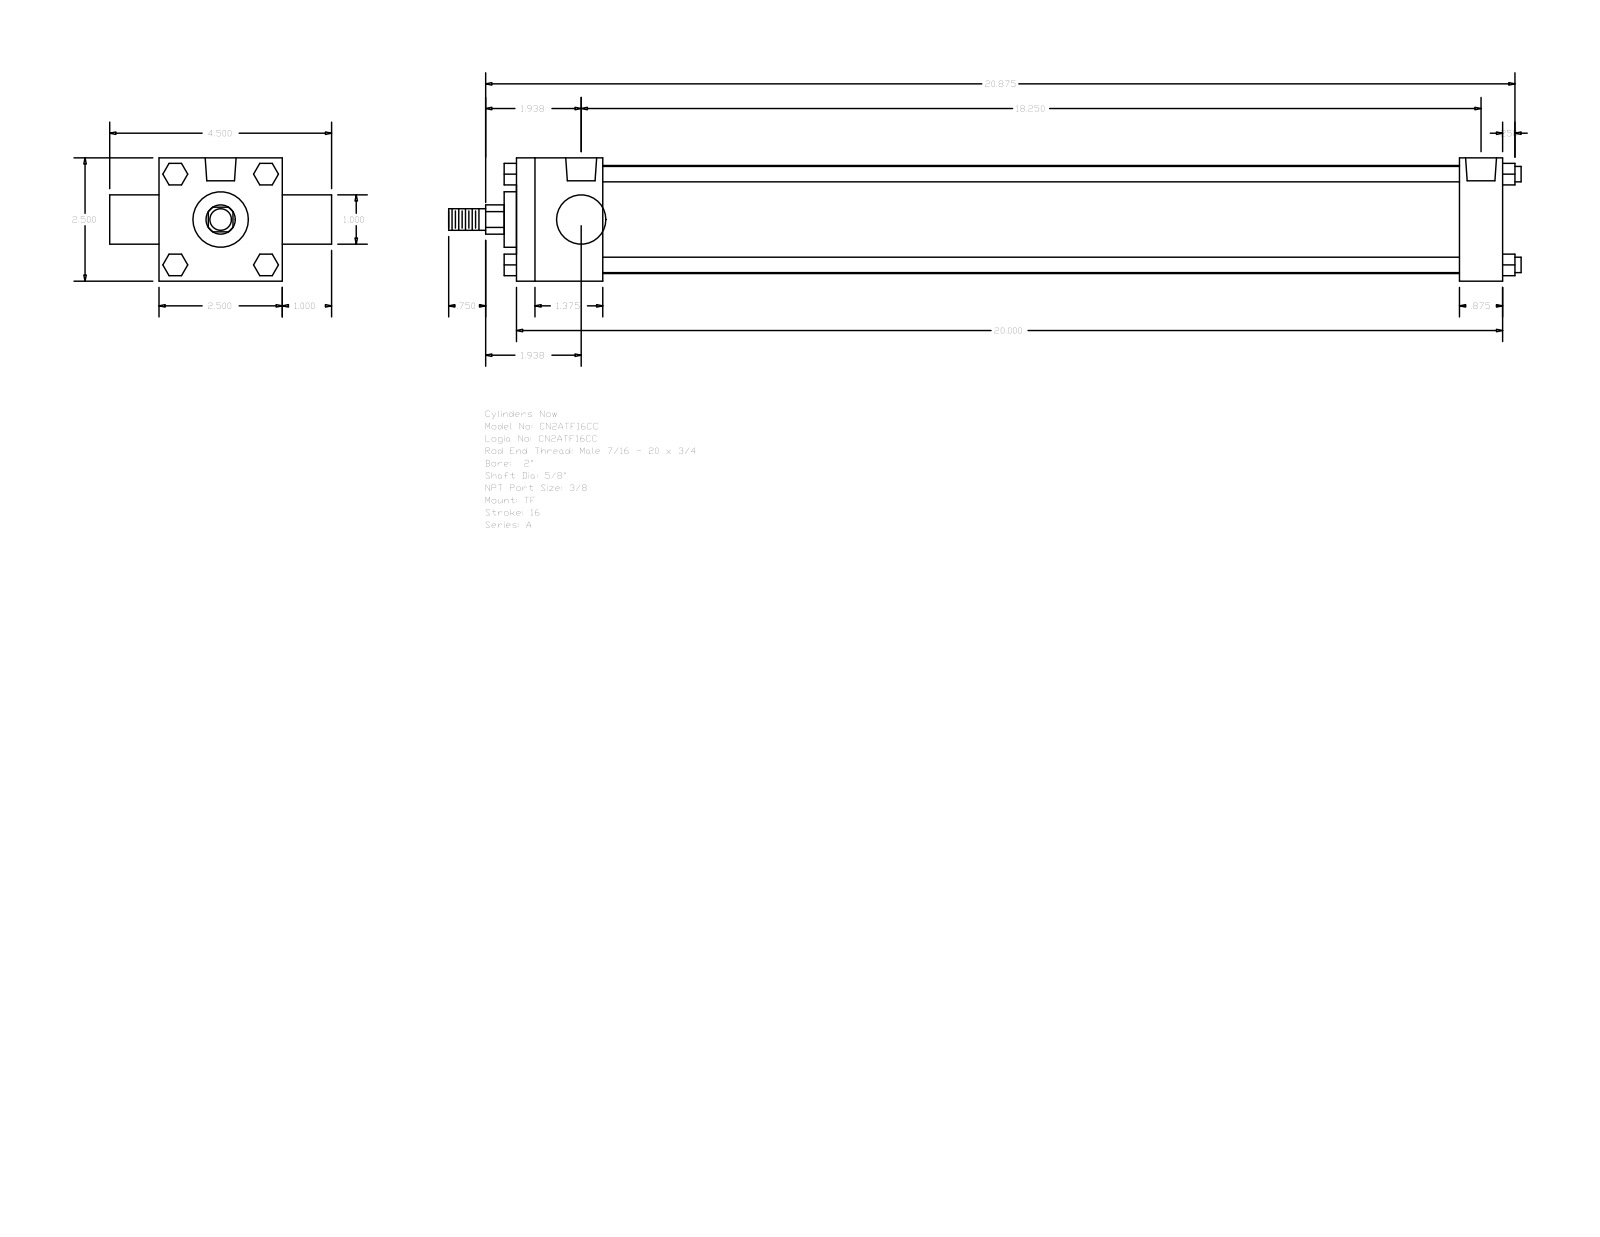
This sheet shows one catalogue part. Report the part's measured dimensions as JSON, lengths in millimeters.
{"part_name": "A_TF__0200_0.625", "step_written_by": "GSSL Pune (CONFIG_CONTROL_DESIGN)", "units": "millimeters", "bodies": {"solids": 0, "faces": 120, "planar": 92, "cylindrical": 28, "other": 0}, "overall_size": [552.45, 114.3, 63.5], "round_holes": [[5.56, 3], [15.93, 2]], "round_bosses_or_shafts": [[7.94, 4], [55.63, 1], [28.57, 1], [25.4, 1], [15.88, 1], [11.11, 1]], "partial_cylinders_radius": [[7.54, 1]], "face_to_face_distances": [63.5, 508, 44.45, 485.77, 441.32, 463.55, 22.23, 25.4, 88.9, 6.35], "hole_center_spacings": [3.97, 3.98, 455.6, 459.57, 459.58, 463.55]}
